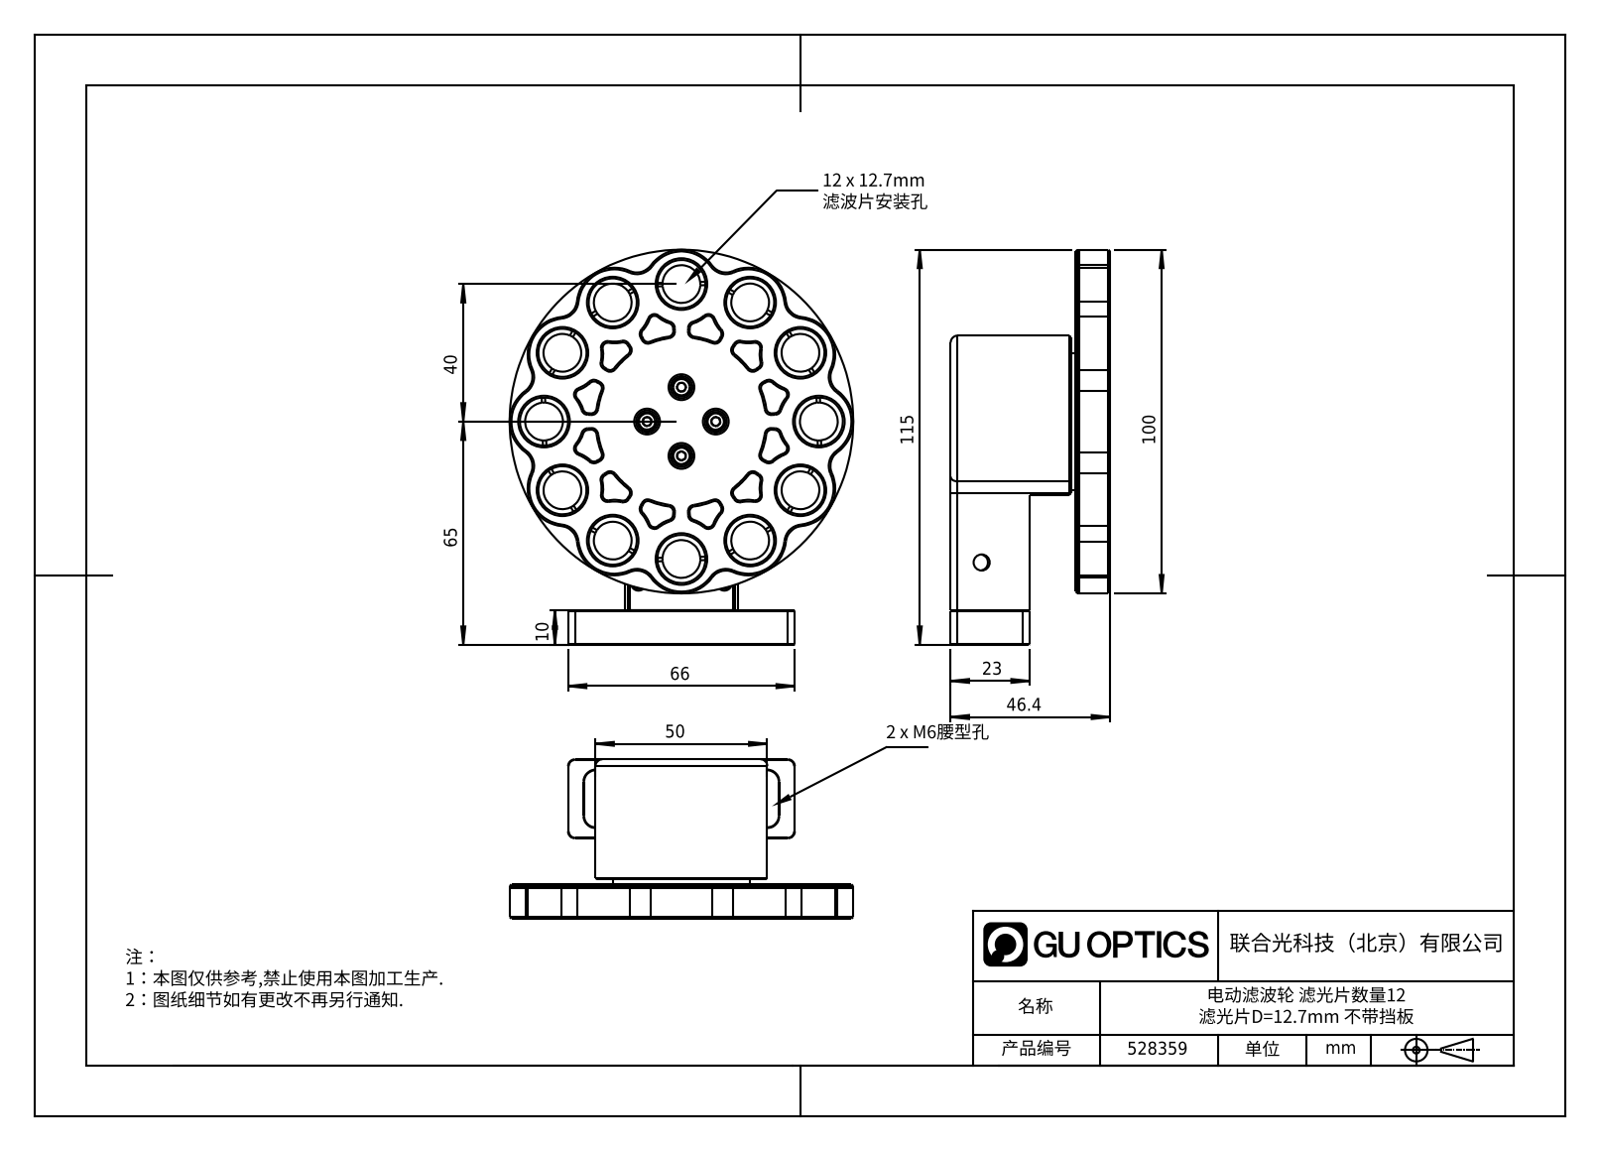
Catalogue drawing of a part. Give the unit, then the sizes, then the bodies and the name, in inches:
Units: inches
Overall size (bounding box): 4.528 × 3.937 × 1.827
Round holes (diameter × count): ⌀0.315 ×4, ⌀0.185 ×1, ⌀1.969 ×1, ⌀3.937 ×1
Round bosses / shafts (diameter × count): ⌀0.551 ×12, ⌀0.433 ×12, ⌀0.256 ×4, ⌀0.217 ×4, ⌀0.205 ×4, ⌀0.138 ×4, ⌀0.276 ×3, ⌀1.575 ×1
Partial cylindrical surfaces — rounded edges, fillets, slot ends (radius × count): R0.059 ×60, R0.012 ×20, R0.197 ×14, R0.433 ×12, R0.079 ×6, R0.13 ×4, R0.02 ×2
Main face-to-face distances: 0.394, 1.433, 1.827, 0.039, 0.354, 1.472, 0.906, 0.528, 0.567, 0.921
Hole centre spacings: 0.472, 1.063, 1.163
Bodies: 0 solids, 809 faces (361 planar, 217 cylindrical, 231 other)
Part name (STEP PRODUCT): 528359
STEP written by: SolidWorks 2020 (CONFIG_CONTROL_DESIGN)
